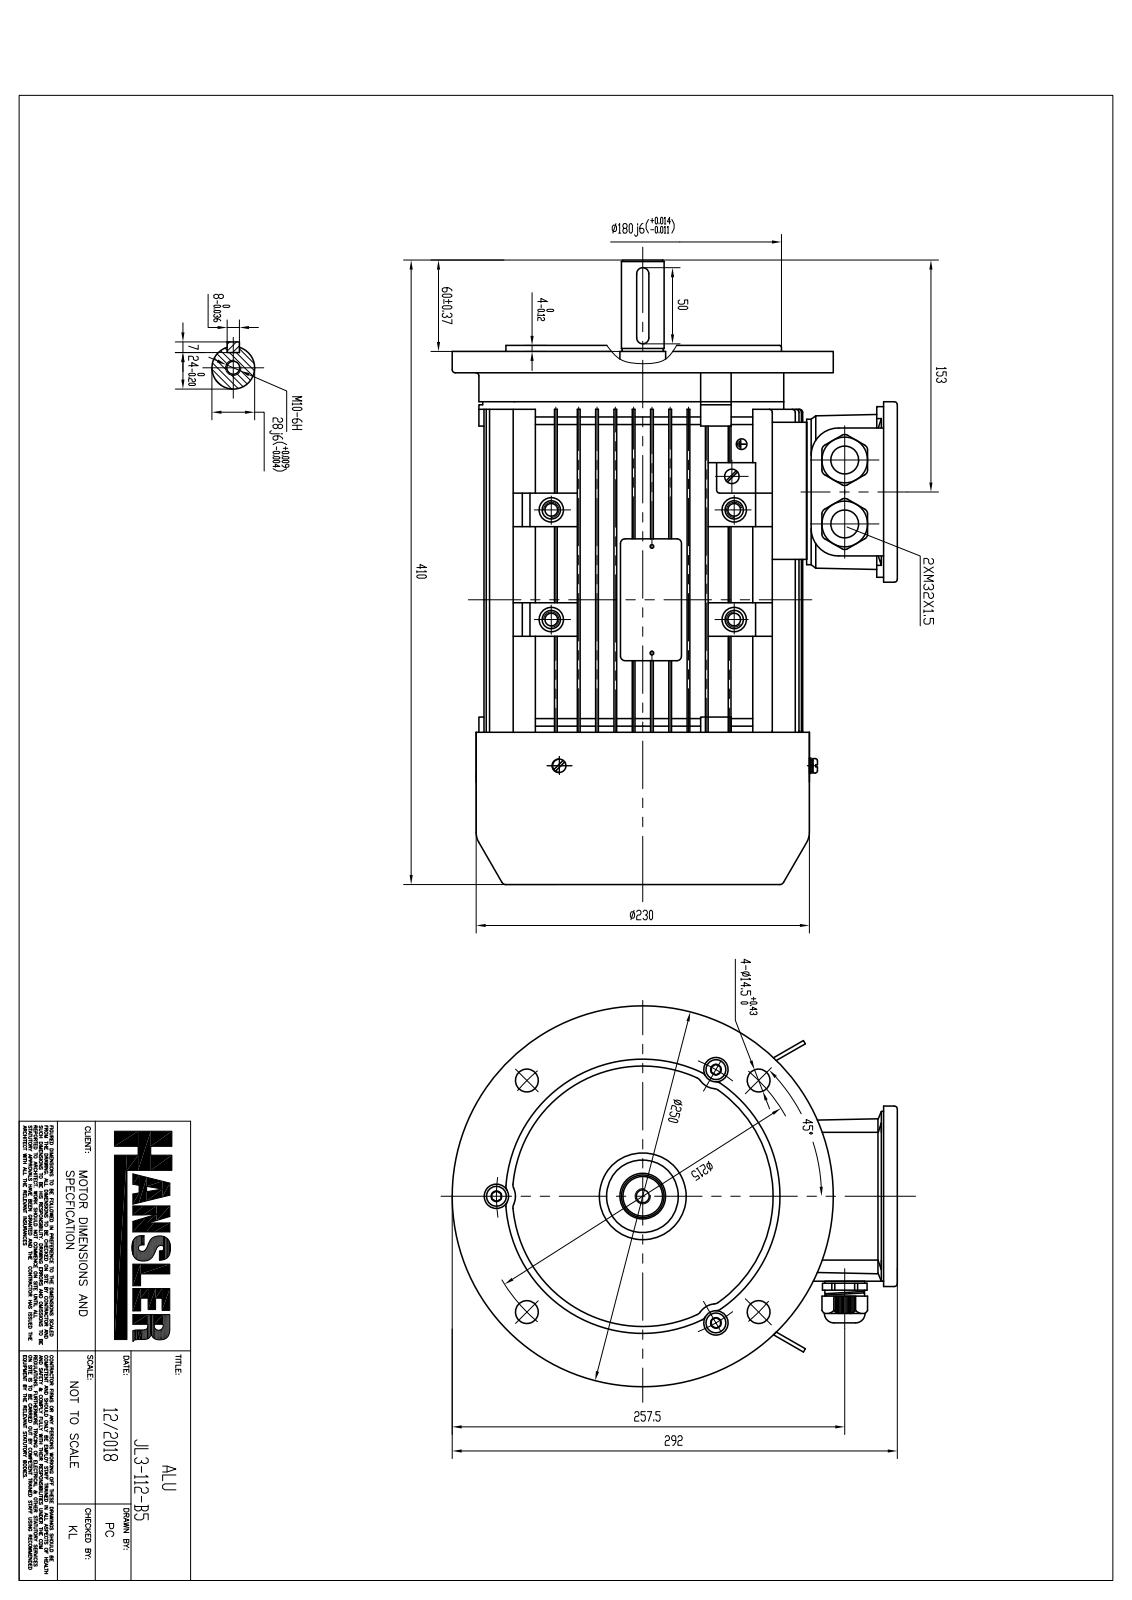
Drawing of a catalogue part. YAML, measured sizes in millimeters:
part_name: "JL3-112-B5"
step_written_by: "SolidWorks 2018 (CONFIG_CONTROL_DESIGN)"
units: millimeters
bodies: {solids: 46, faces: 3635, planar: 1599, cylindrical: 1588, other: 448}
overall_size: [395, 301.66, 250]
volume: 2864000
surface_area: 1237000
round_holes:
  - {diameter: 8, count: 12}
  - {diameter: 5.8, count: 10}
  - {diameter: 18, count: 8}
  - {diameter: 16, count: 7}
  - {diameter: 5, count: 6}
  - {diameter: 4, count: 4}
  - {diameter: 5.25, count: 4}
  - {diameter: 5.3, count: 4}
  - {diameter: 10, count: 4}
  - {diameter: 3.85, count: 3}
  - {diameter: 8.39, count: 3}
  - {diameter: 8.58, count: 2}
round_bosses_or_shafts:
  - {diameter: 12, count: 8}
  - {diameter: 5, count: 8}
  - {diameter: 10, count: 4}
  - {diameter: 9.5, count: 4}
  - {diameter: 7.85, count: 4}
  - {diameter: 4.48, count: 4}
  - {diameter: 13, count: 3}
  - {diameter: 12.59, count: 3}
partial_cylinders:
  - {radius: 0.5, count: 656}
  - {radius: 2, count: 32}
  - {radius: 3, count: 31}
  - {radius: 5, count: 25}
  - {radius: 4, count: 20}
  - {radius: 0.3, count: 16}
  - {radius: 0.2, count: 12}
  - {radius: 1, count: 8}
face_to_face_distances: [1.8, 15, 14, 100, 85, 28, 16.8, 71, 42, 115]
hole_center_spacings: [84.34, 98, 21.26, 43.86, 1.41, 18, 20.74, 21.21]
